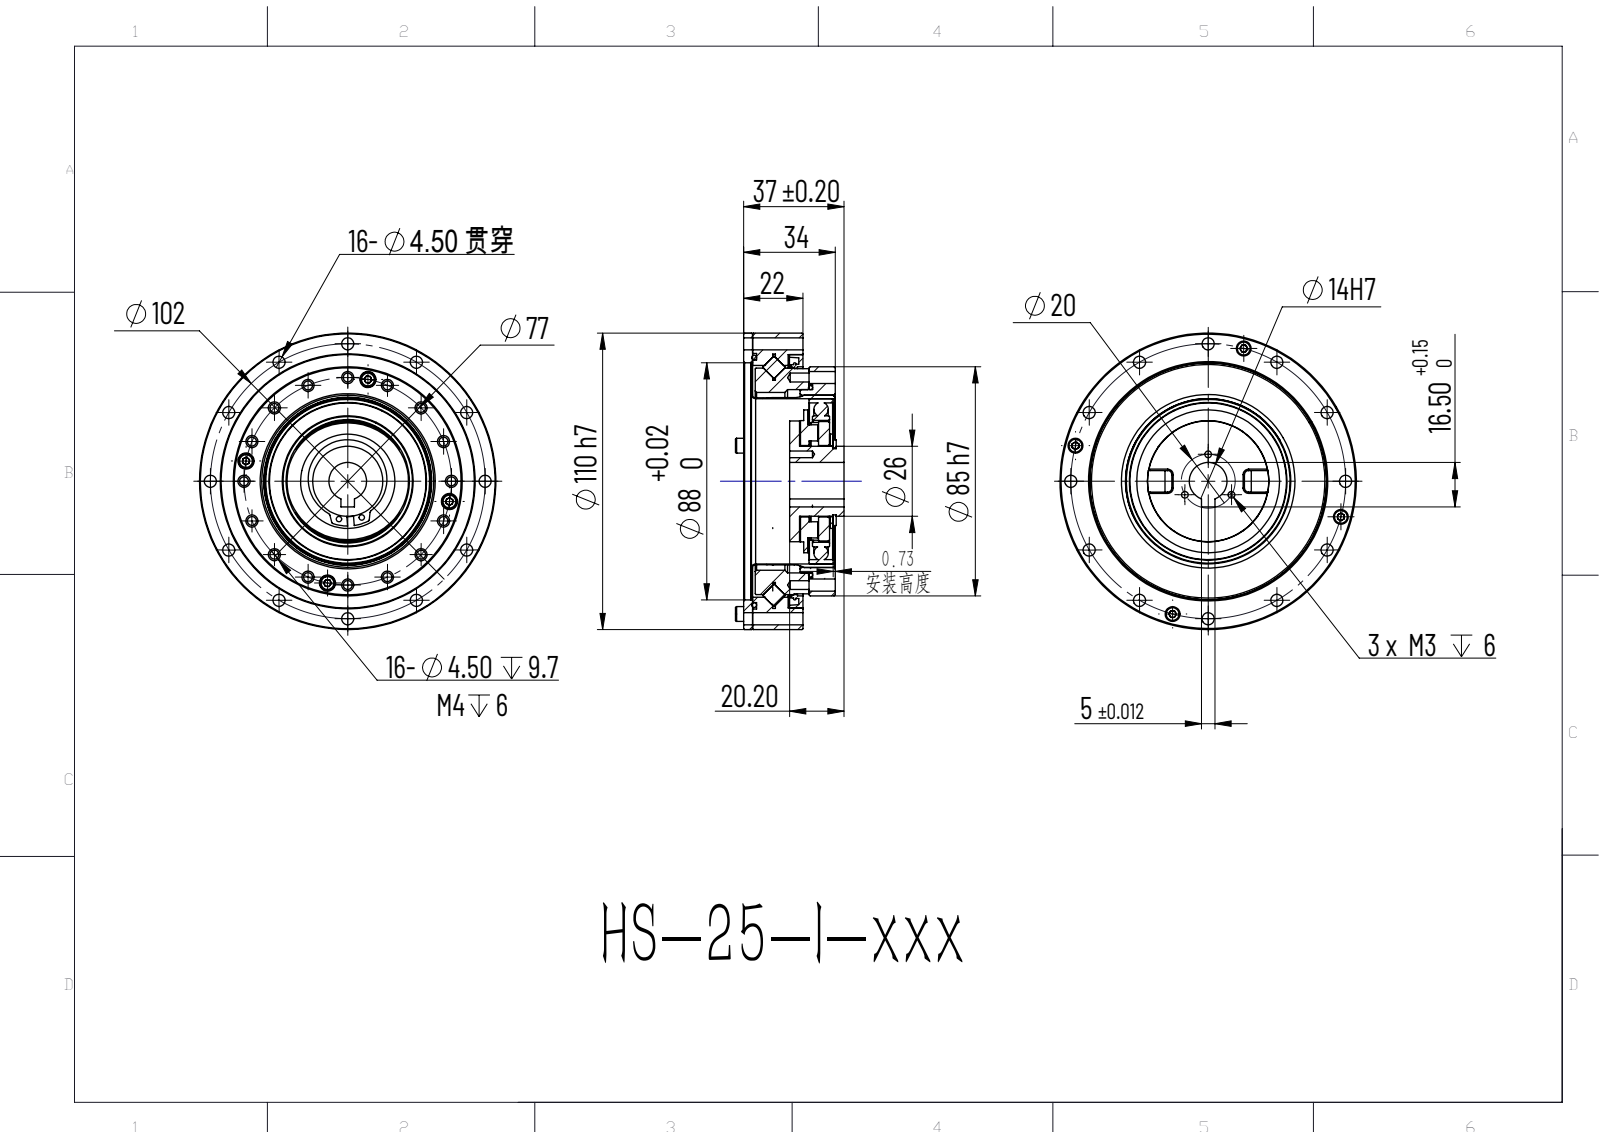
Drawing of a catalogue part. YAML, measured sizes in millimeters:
part_name: "HS-25-I; ????-STXB-25080; hexagon socket head cap screws gb_GB_FASTENER_SCREWS_HSHCS M3X8-C; O????-?71X?1.5 (+8 more)"
step_written_by: "ONSHAPE BY PTC INC, 1.201 (AP242_MANAGED_MODEL_BASED_3D_ENGINEERING_MIM_LF)"
units: millimeters
bodies: {solids: 96, faces: 1035, planar: 565, cylindrical: 272, other: 198}
overall_size: [110, 110, 40.29]
volume: 171806
surface_area: 126352
round_holes:
  - {diameter: 4.5, count: 28}
  - {diameter: 3.3, count: 16}
  - {diameter: 2.5, count: 11}
  - {diameter: 3.4, count: 4}
  - {diameter: 3.5, count: 4}
  - {diameter: 6, count: 4}
  - {diameter: 2, count: 2}
  - {diameter: 2.05, count: 1}
  - {diameter: 2.9, count: 1}
  - {diameter: 5, count: 1}
  - {diameter: 14, count: 1}
  - {diameter: 24.2, count: 1}
round_bosses_or_shafts:
  - {diameter: 6, count: 36}
  - {diameter: 5.5, count: 8}
  - {diameter: 3, count: 8}
  - {diameter: 110, count: 1}
  - {diameter: 90, count: 1}
  - {diameter: 84, count: 1}
  - {diameter: 83.5, count: 1}
  - {diameter: 75, count: 1}
partial_cylinders:
  - {radius: 3.02, count: 36}
  - {radius: 1.5, count: 4}
  - {radius: 0.5, count: 2}
  - {radius: 1, count: 2}
  - {radius: 16.6, count: 1}
face_to_face_distances: [18.7, 2.3, 3.3, 22, 24.3, 21, 1.5, 2.91, 0.39, 19.09]
hole_center_spacings: [15.02, 38.5, 51, 54.45, 64.02, 29.46, 71.13, 22.35]
